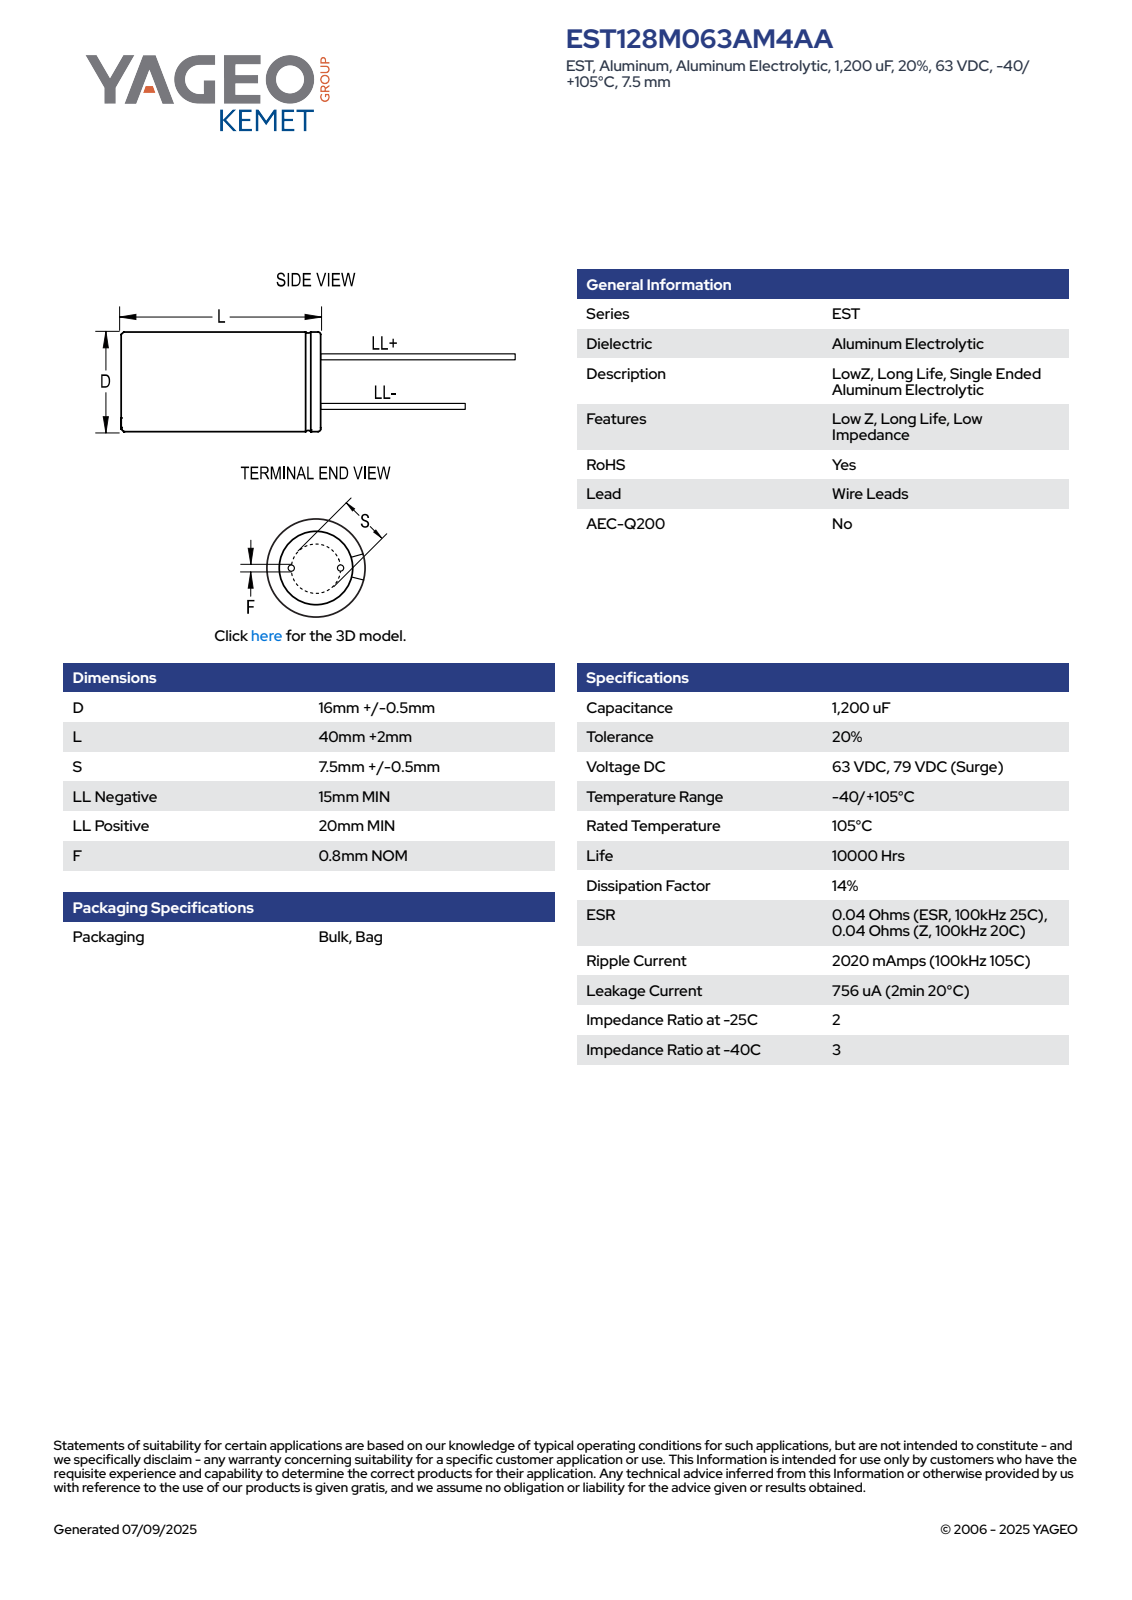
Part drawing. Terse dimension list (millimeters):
name: CAR_KLP_16X40_D16.5L42S7.5F0.8
written by: SolidWorks 2014 (AUTOMOTIVE_DESIGN)
unit: mm
bodies: 4 solids, 75 faces (61 planar, 8 cylindrical, 6 other)
size: 62.01 × 16.5 × 16.5
volume: 8 952 mm³; area: 2 756 mm²
bosses: 2× ⌀0.8, 1× ⌀16.5
face distances: 42, 42.01, 5, 57.01, 62.01, 57, 62, 15, 20, 2.22
